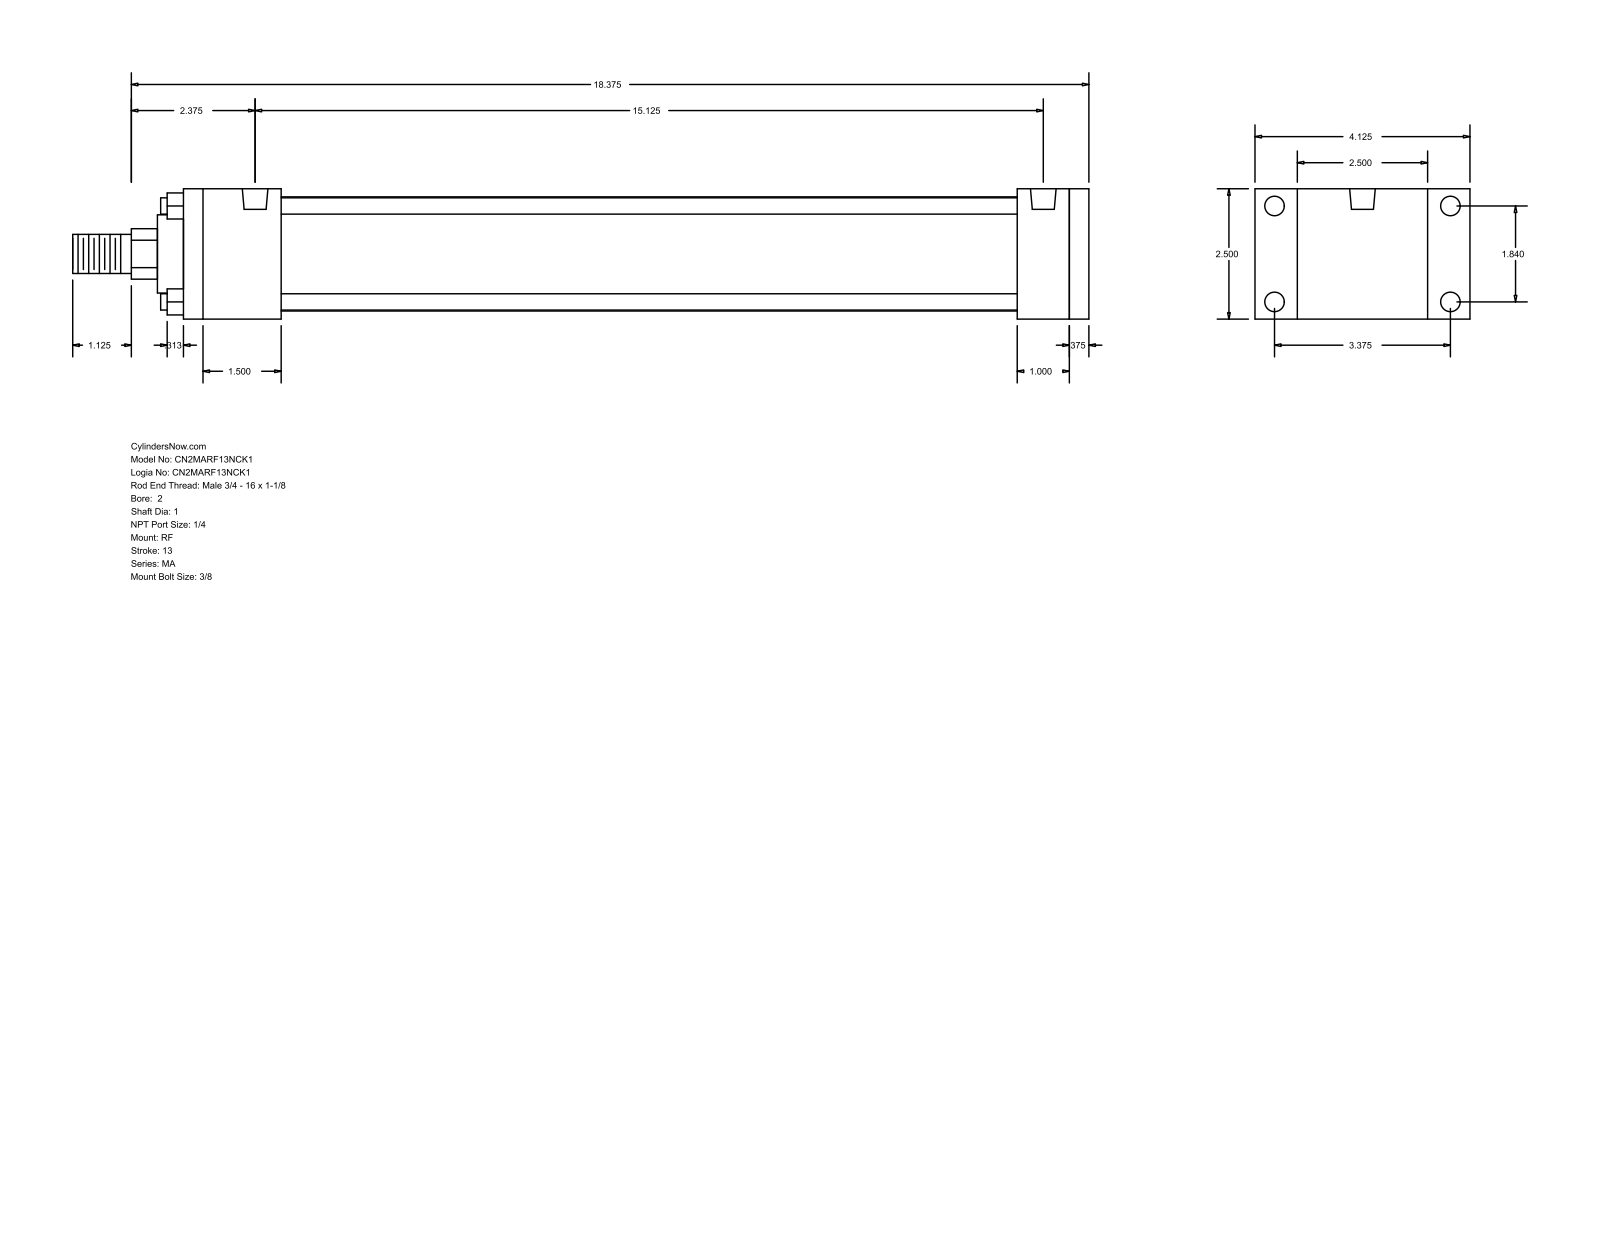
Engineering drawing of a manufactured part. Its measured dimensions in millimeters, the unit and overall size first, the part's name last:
Units: millimetres
Overall size (bounding box): 495.3 × 104.78 × 63.5
Round holes (diameter × count): ⌀7.94 ×4, ⌀9.53 ×4, ⌀12.49 ×2
Round bosses / shafts (diameter × count): ⌀7.94 ×4, ⌀55.63 ×1, ⌀38.1 ×1, ⌀25.4 ×1, ⌀19.05 ×1
Partial cylindrical surfaces — rounded edges, fillets, slot ends (radius × count): R12.29 ×1
Main face-to-face distances: 63.5, 431.8, 9.53, 441.33, 25.4, 20.64, 12.7, 47.63, 384.17, 393.7
Hole centre spacings: 46.74, 85.72, 97.63, 384.17
Bodies: 0 solids, 92 faces (64 planar, 28 cylindrical, 0 other)
Part name (STEP PRODUCT): MA_RF__0200_1
STEP written by: GSSL Pune (CONFIG_CONTROL_DESIGN)
